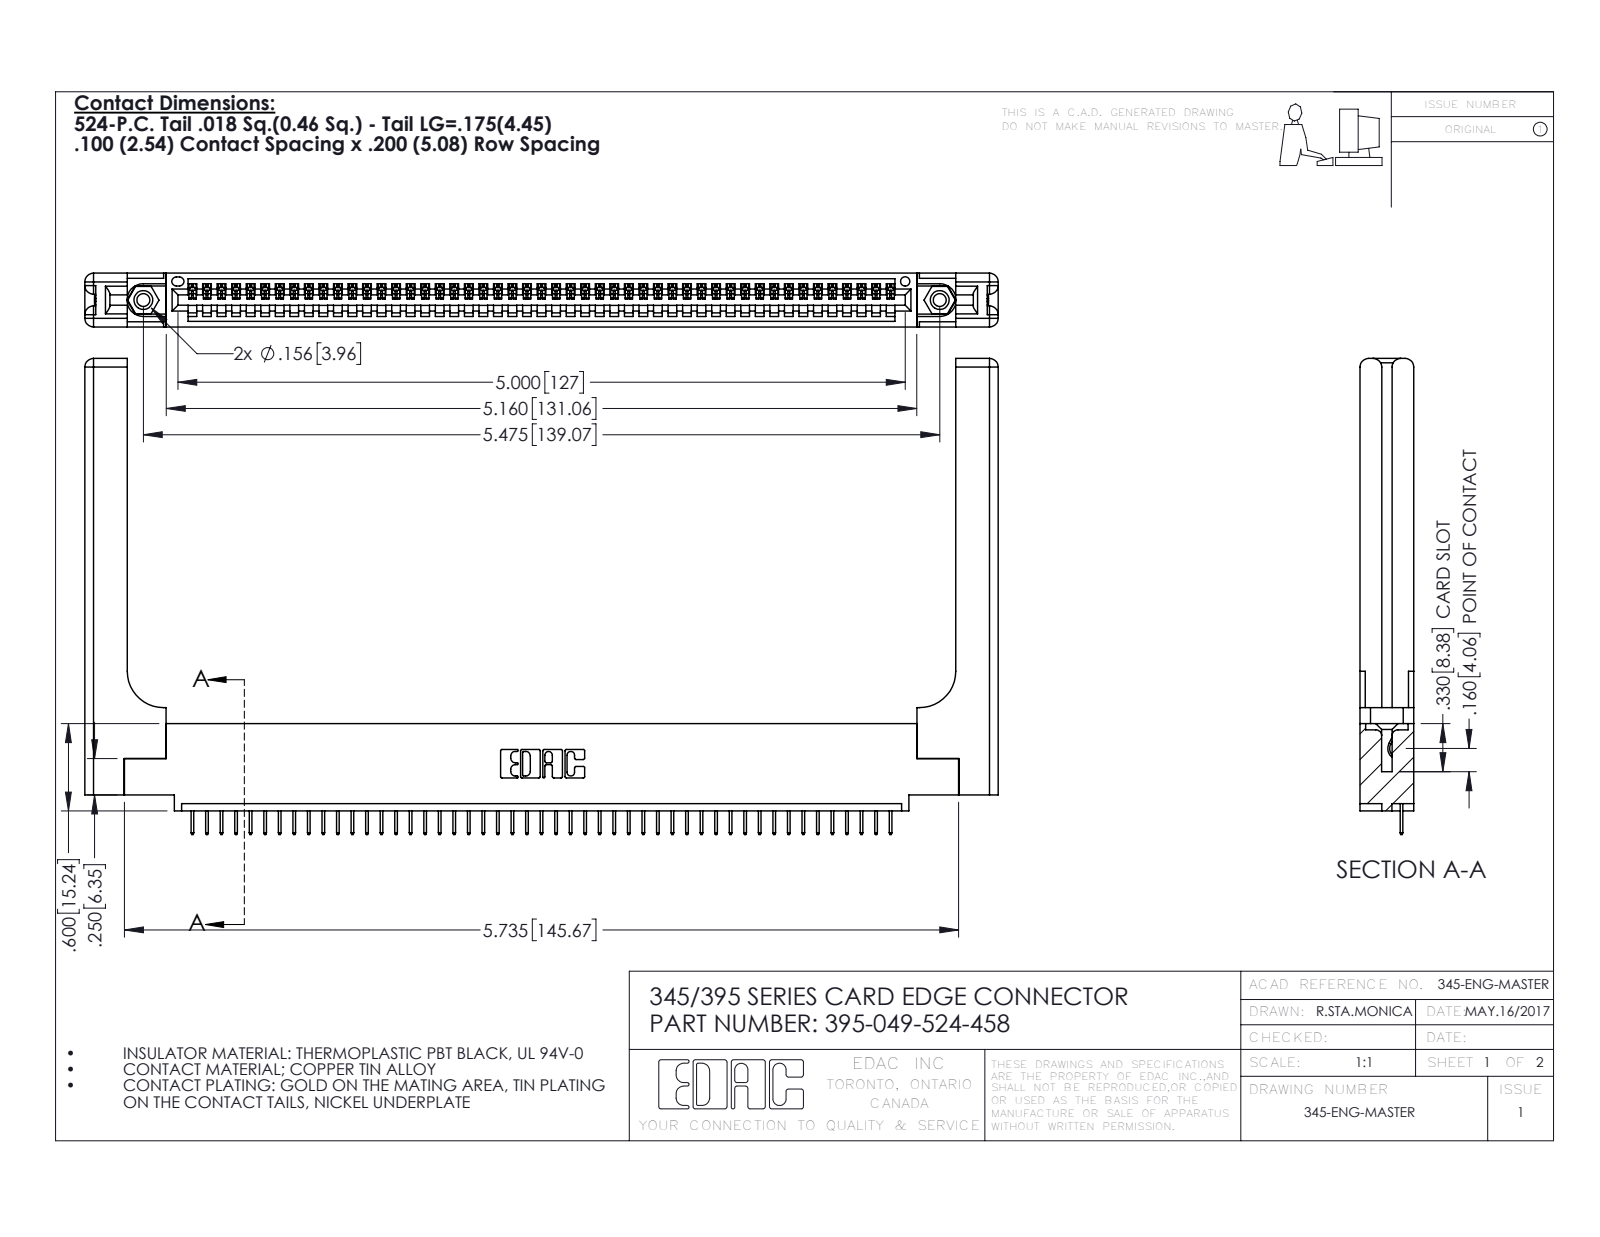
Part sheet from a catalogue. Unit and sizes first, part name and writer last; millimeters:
Units: millimetres
Overall size (bounding box): 159.5 × 83.1 × 9.4
Round holes (diameter × count): ⌀2.3 ×2, ⌀3.2 ×2, ⌀4 ×2, ⌀1.6 ×1
Round bosses / shafts (diameter × count): ⌀3.9 ×2
Partial cylindrical surfaces — rounded edges, fillets, slot ends (radius × count): R0.2 ×98, R0.3 ×22, R1.5 ×16, R0.2 ×6, R0.8 ×6, R0.7 ×3, R0.8 ×2, R0.8 ×2
Main face-to-face distances: 9.4, 1.8, 7.6, 2.5, 6.9, 0.6, 5.1, 5.7, 3.8, 3.8
Hole centre spacings: 6.9, 133.1, 139.1
Volume: 23 450 mm³ · Surface area: 24 720 mm²
Bodies: 54 solids, 3424 faces (2486 planar, 878 cylindrical, 60 other)
Part name (STEP PRODUCT): 395-049-524-458; 345-292-001_345-293-124; 345-250-001_345-250-001-102; 345-220-058_345-220-058 (+1 more)
STEP written by: SolidWorks 2016 (CONFIG_CONTROL_DESIGN)
